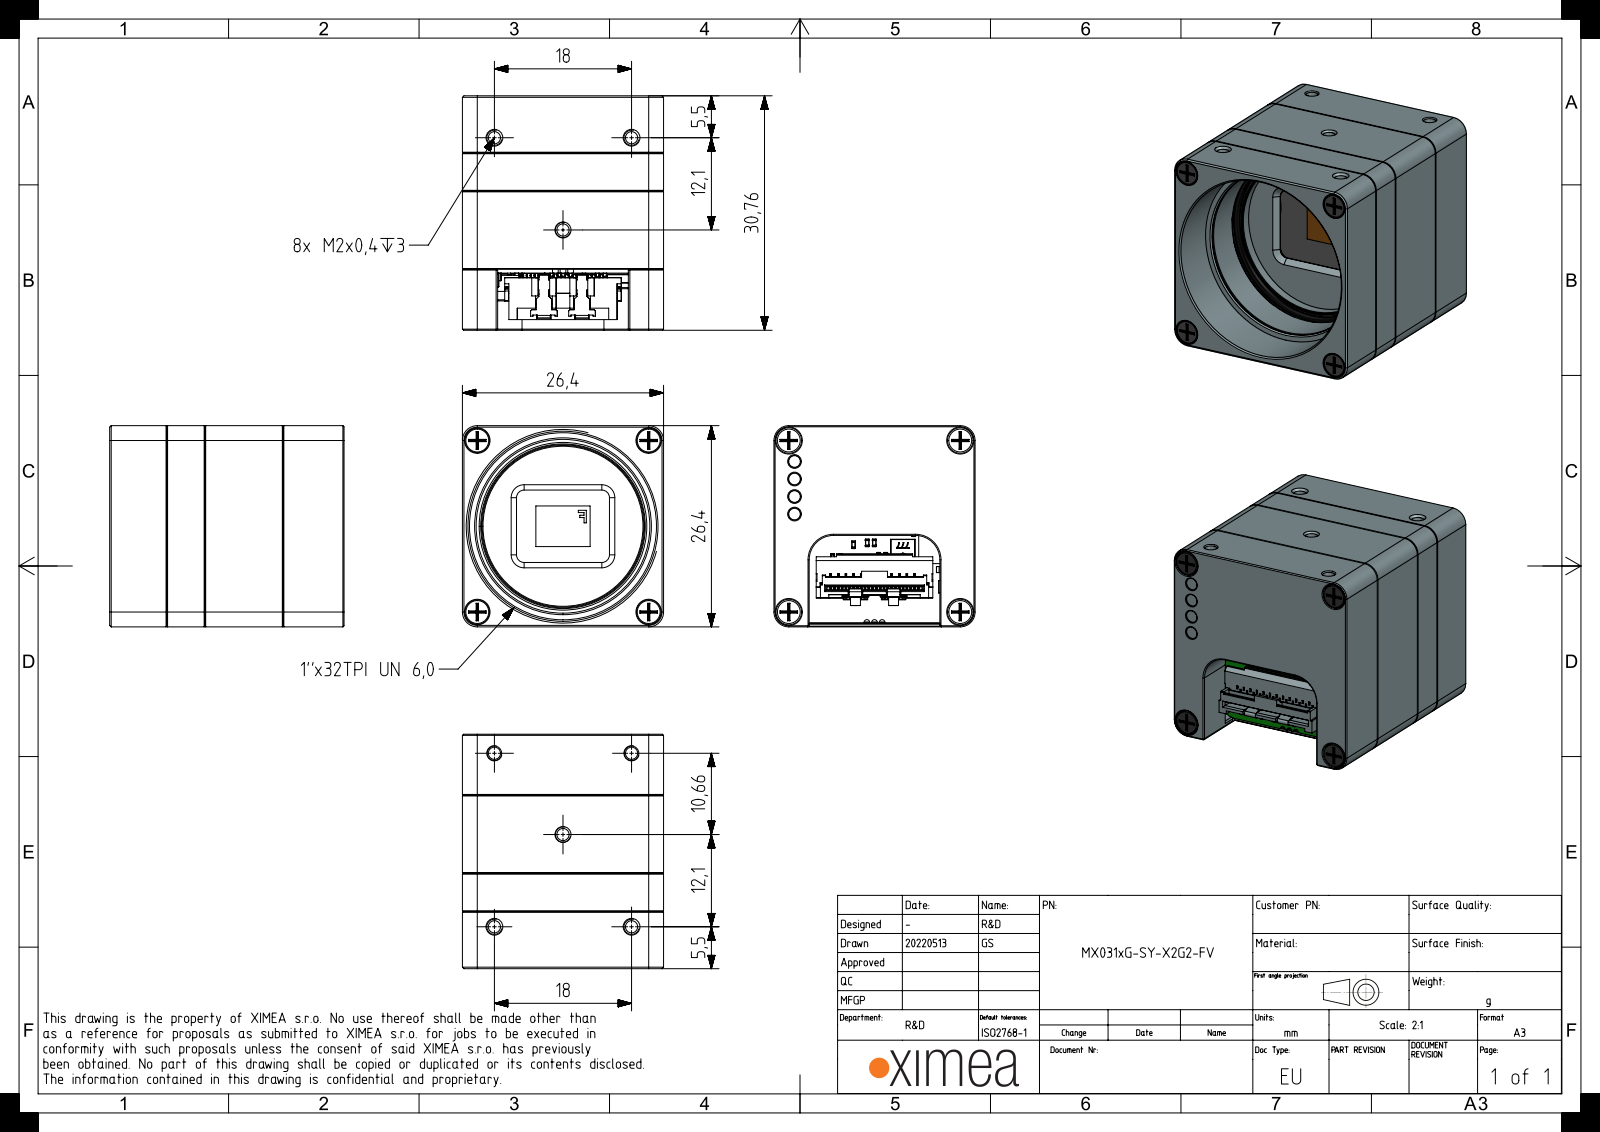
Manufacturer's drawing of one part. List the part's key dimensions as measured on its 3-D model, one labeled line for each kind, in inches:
Part name (STEP PRODUCT): SROB-M2x10-CUST; MECH-MX-THERMAL-PAD-10X10; MECH-LIGHTPIPE-1.63x4.14; MX-X2G2-MAIN-FV-PCA (+8 more)
STEP written by: SIEMENS PLM Software NX 1907 (AUTOMOTIVE_DESIGN)
Units: inches
Bodies: 32 solids, 7513 faces (5230 planar, 2012 cylindrical, 271 other)
Overall size (bounding box): 1.211 × 1.039 × 1.039
Volume: 0.635 in³ · Surface area: 27.27 in²
Round holes (diameter × count): ⌀0.063 ×13, ⌀0.035 ×4, ⌀0.071 ×4, ⌀0.079 ×4, ⌀0.083 ×4, ⌀0.118 ×4, ⌀0.126 ×4, ⌀0.132 ×4, ⌀0.051 ×2, ⌀0.073 ×1, ⌀0.073 ×1, ⌀0.827 ×1
Round bosses / shafts (diameter × count): ⌀0.075 ×4, ⌀0.064 ×4, ⌀0.033 ×4, ⌀0.118 ×2, ⌀0.063 ×2, ⌀0.984 ×1, ⌀0.85 ×1
Partial cylindrical surfaces — rounded edges, fillets, slot ends (radius × count): R0.059 ×19, R0.013 ×16, R0.006 ×14, R0.039 ×14, R0.004 ×12, R0.015 ×12, R0.051 ×8, R0.008 ×5
Main face-to-face distances: 0.039, 1.039, 0.138, 0.447, 0.27, 0.304, 0.165, 0.178, 0.408, 0.404
Hole centre spacings: 0.15, 0.508, 0.626, 0.739, 0.869, 0.886, 1.131, 0.091
